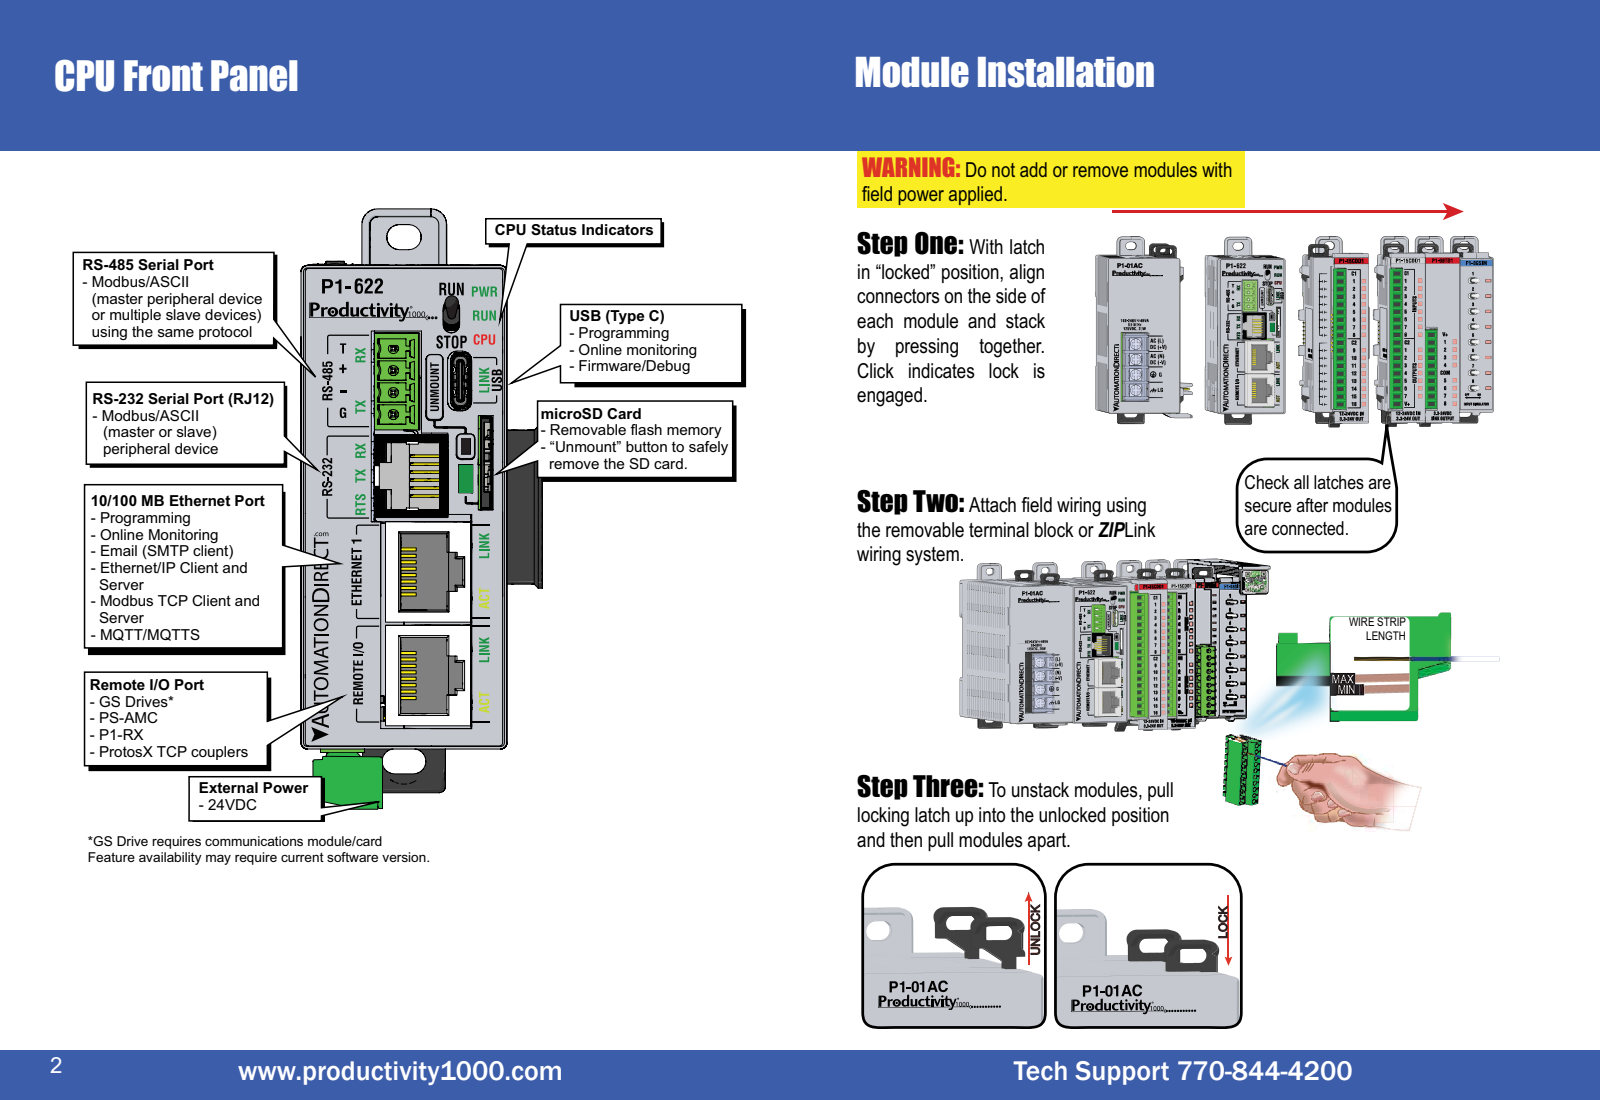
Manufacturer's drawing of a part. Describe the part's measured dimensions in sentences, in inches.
The part is named "P1-622". Its 3-D file was written by "SolidWorks 2021 (AUTOMOTIVE_DESIGN)". It is 1 solid with 5461 faces: 2780 planar, 899 cylindrical and 1782 other. Overall it measures 3.821 by 3.762 by 1.448 inches. Its volume is 1.585 cubic inches and its surface area 81.58 square inches. Round holes: 2 of diameter 0.024. Partial cylindrical surfaces (rounded edges, fillets, slot ends): 224 of radius 0.01, 81 of radius 0.02, 47 of radius 0.039, 35 of radius 0.008, 13 of radius 0.016, 12 of radius 0.012, 11 of radius 0.059, 8 of radius 0.004. The main face-to-face distances are 0.017, 1.274, 1.257, 0.017, 1.291, 1.29, 1.273, 2.997, 3.109, 1.29. The hole center spacings are 0.079, 0.413.
